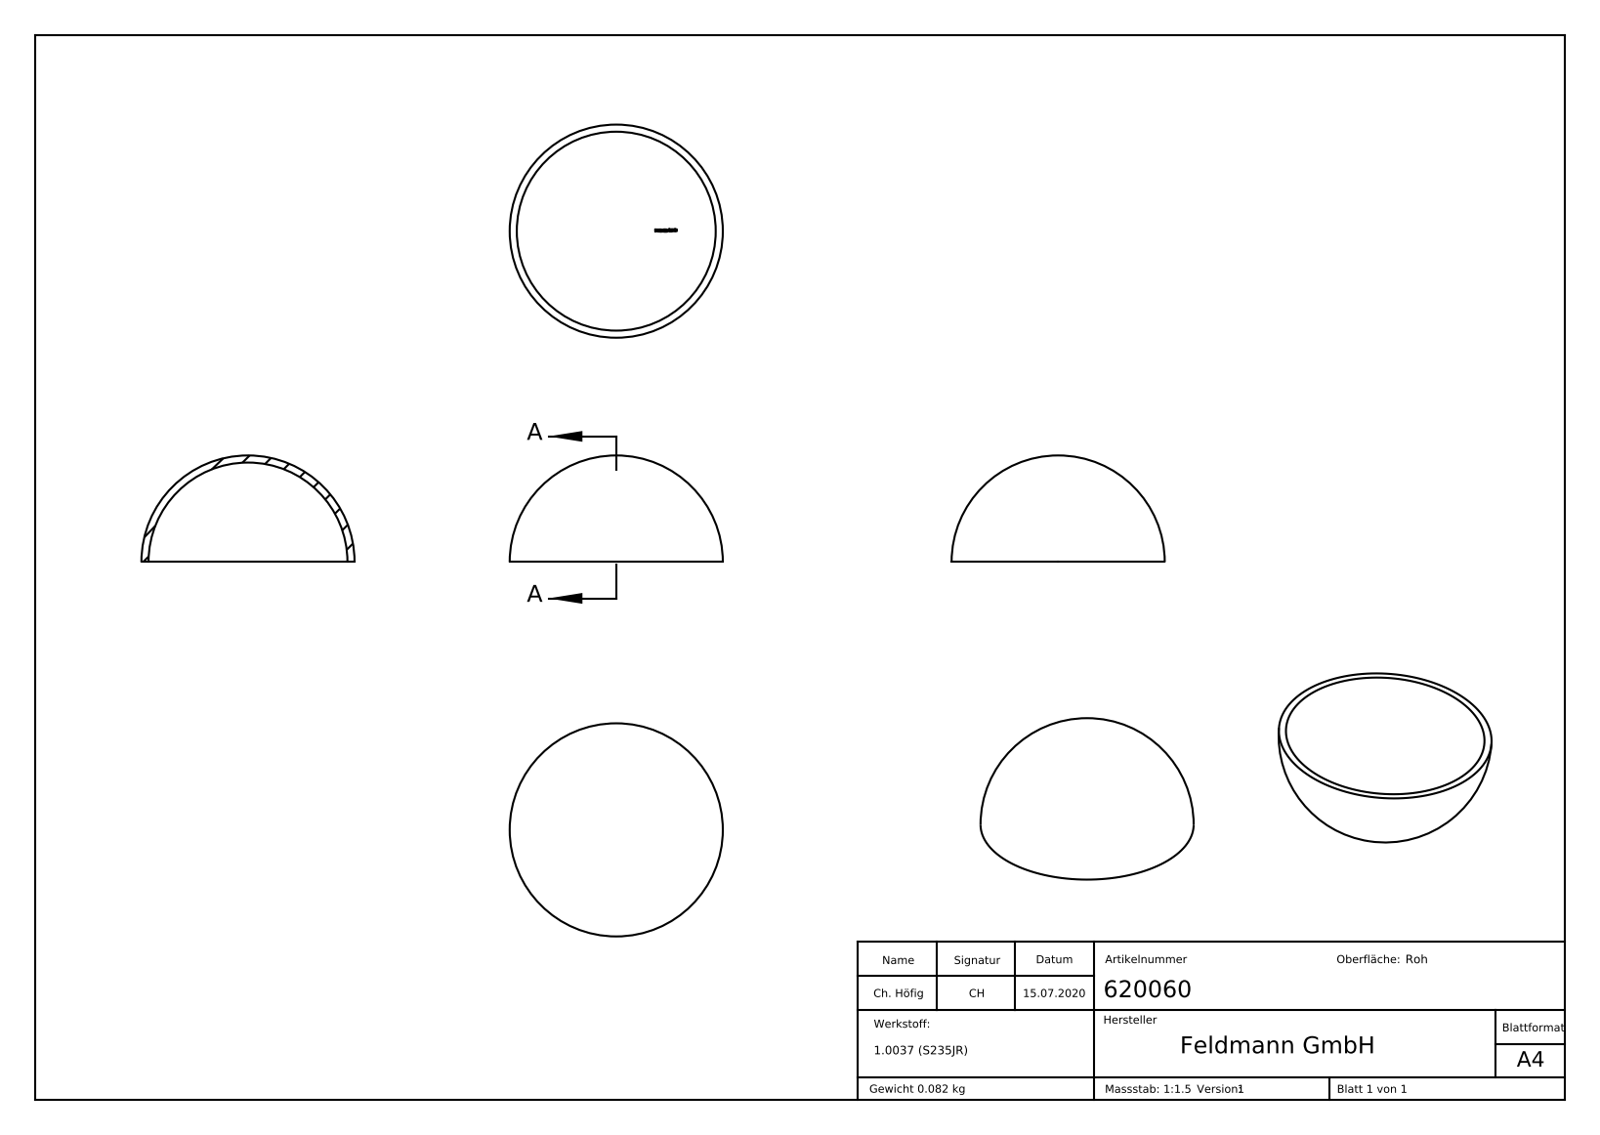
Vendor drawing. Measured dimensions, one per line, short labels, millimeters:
name: 620060
written by: SolidWorks 2018 (CONFIG_CONTROL_DESIGN)
unit: mm
bodies: 1 solid, 190 faces (67 planar, 0 cylindrical, 123 other)
size: 60 × 60 × 30
volume: 10 572 mm³; area: 10 949 mm²
face distances: 1.19, 0.55, 0.5, 0.81, 0.45, 0.66, 1.36, 1.74, 1.31, 0.53
